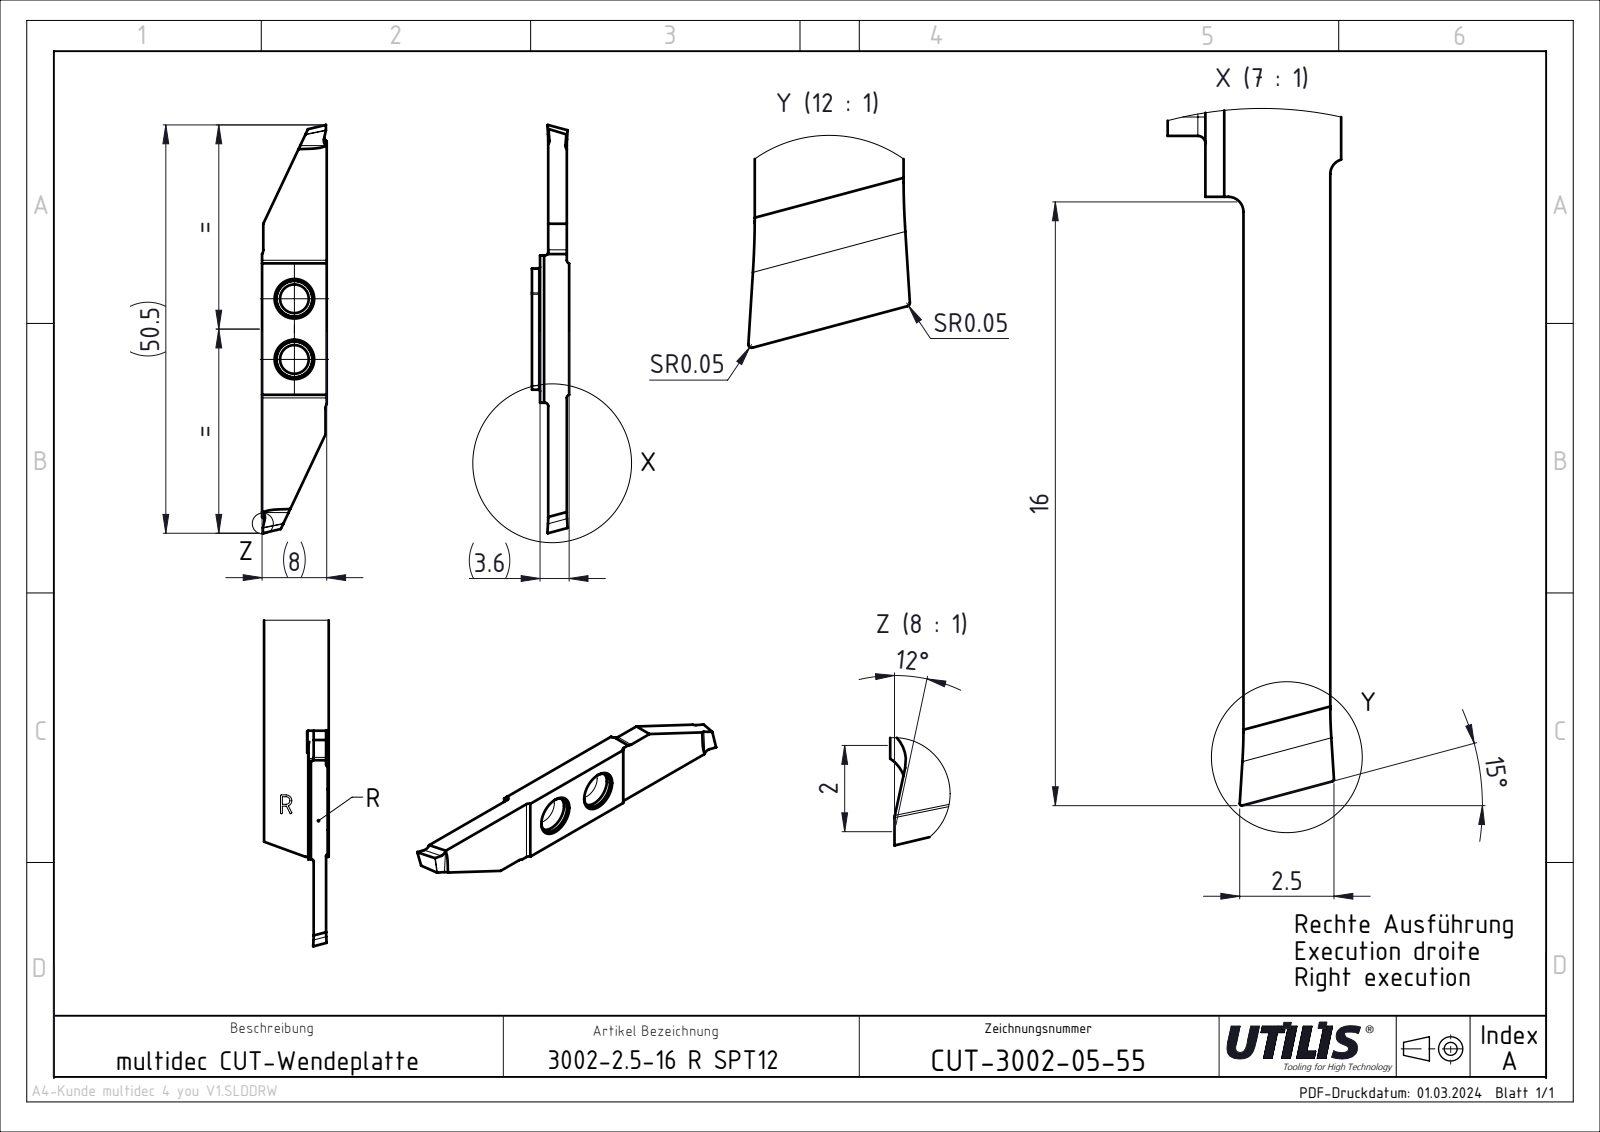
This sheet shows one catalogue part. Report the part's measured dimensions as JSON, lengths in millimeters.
{"part_name": "CUT-3002 SPT Slim_and_Deep; ASME Y14.5", "step_written_by": "SolidWorks 2023 SP4 || FormatWorks Professional (AP242_MANAGED_MODEL_BASED_3D_ENGINEERING_MIM_LF)", "units": "millimeters", "bodies": {"solids": 1, "faces": 36, "planar": 22, "cylindrical": 14, "other": 0}, "overall_size": [50.5, 8, 3.6], "volume_mm3": 864, "surface_area_mm2": 993, "round_holes": [[3.55, 2]], "partial_cylinders_radius": [[0.4, 4], [1, 2]], "face_to_face_distances": [2.3, 2.59, 1.01, 3.31, 3.6, 8, 18.09, 7.85, 7.7, 18.22], "hole_center_spacings": [7.5]}
